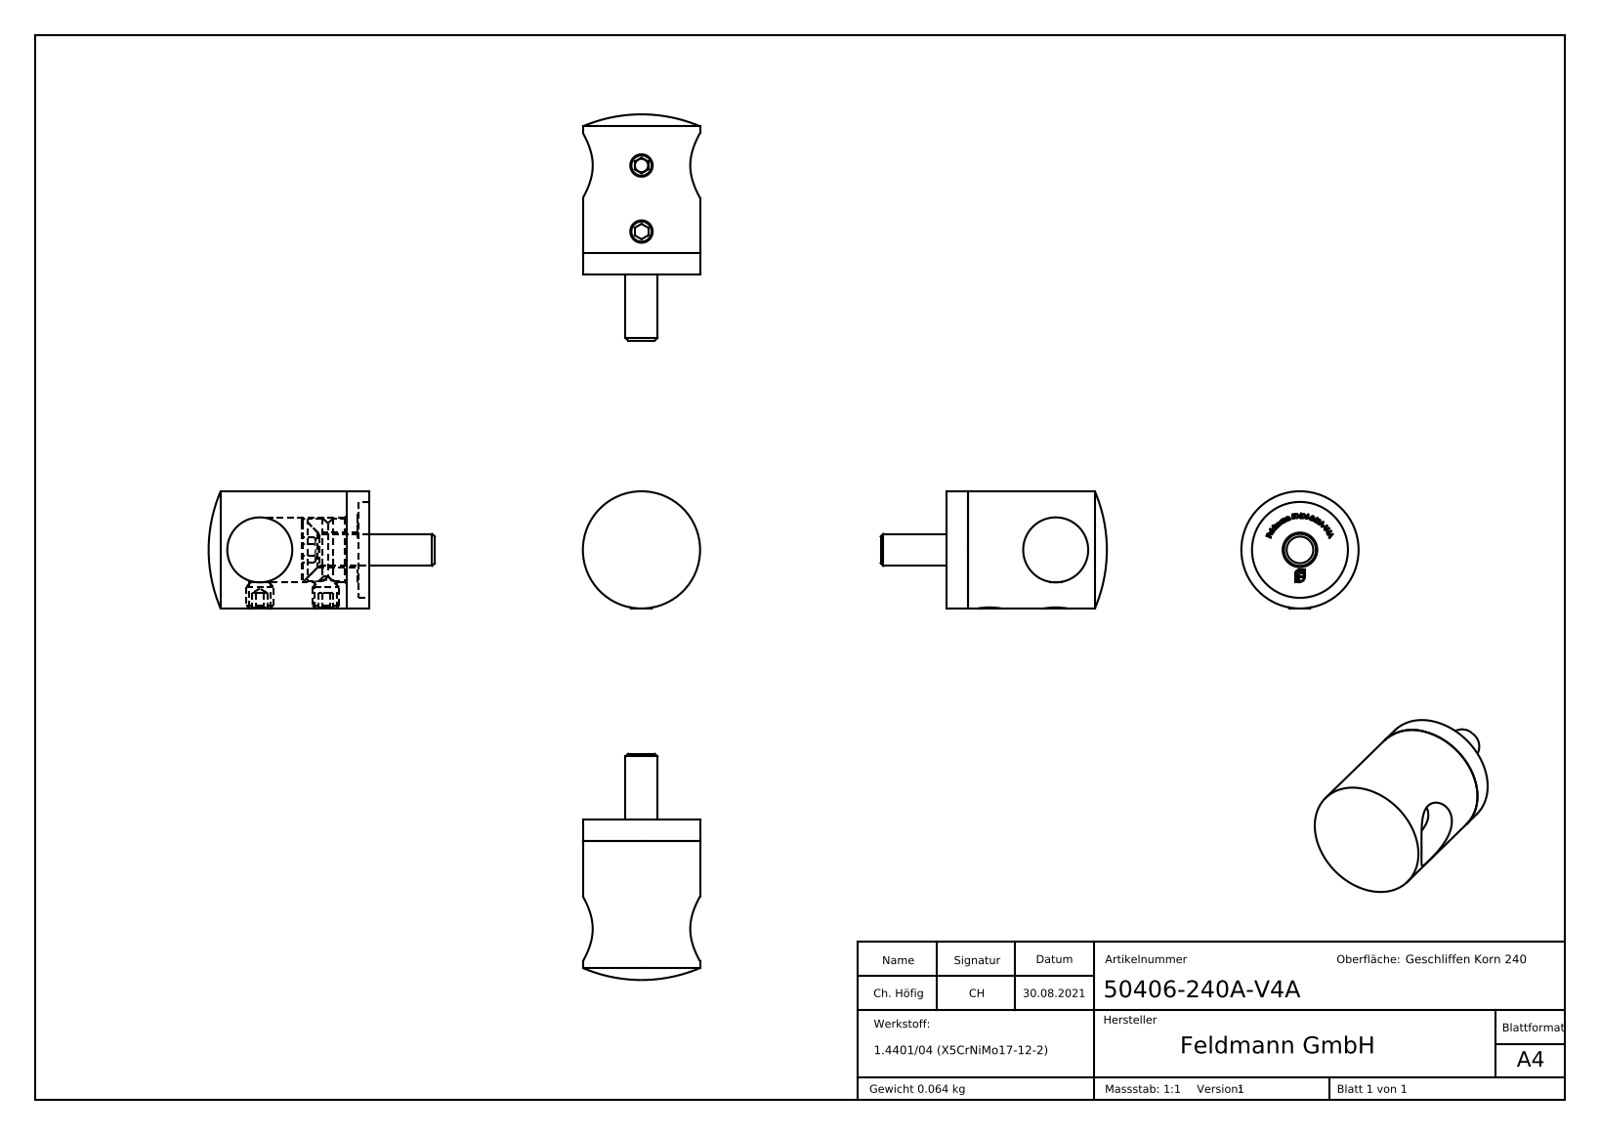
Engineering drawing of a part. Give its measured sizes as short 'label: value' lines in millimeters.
name: DIN 7991 Konfig_M6x25; Oberteil; DIN 7991 Konfig; DIN913 (+7 more)
written by: SolidWorks 2018 (CONFIG_CONTROL_DESIGN)
unit: mm
bodies: 5 solids, 383 faces (238 planar, 14 cylindrical, 131 other)
size: 70 × 42.45 × 22
volume: 8 020 mm³; area: 5 774 mm²
holes: 2× ⌀4.2, 1× ⌀6.5, 1× ⌀12, 1× ⌀12.2, 1× ⌀18
bosses: 2× ⌀5, 1× ⌀22, 1× ⌀11.9, 1× ⌀6
face distances: 2.1, 2, 4.1, 12.65, 10.65, 8.55, 2.5, 1.05, 11.6, 9.6
hole spacings: 12.4
